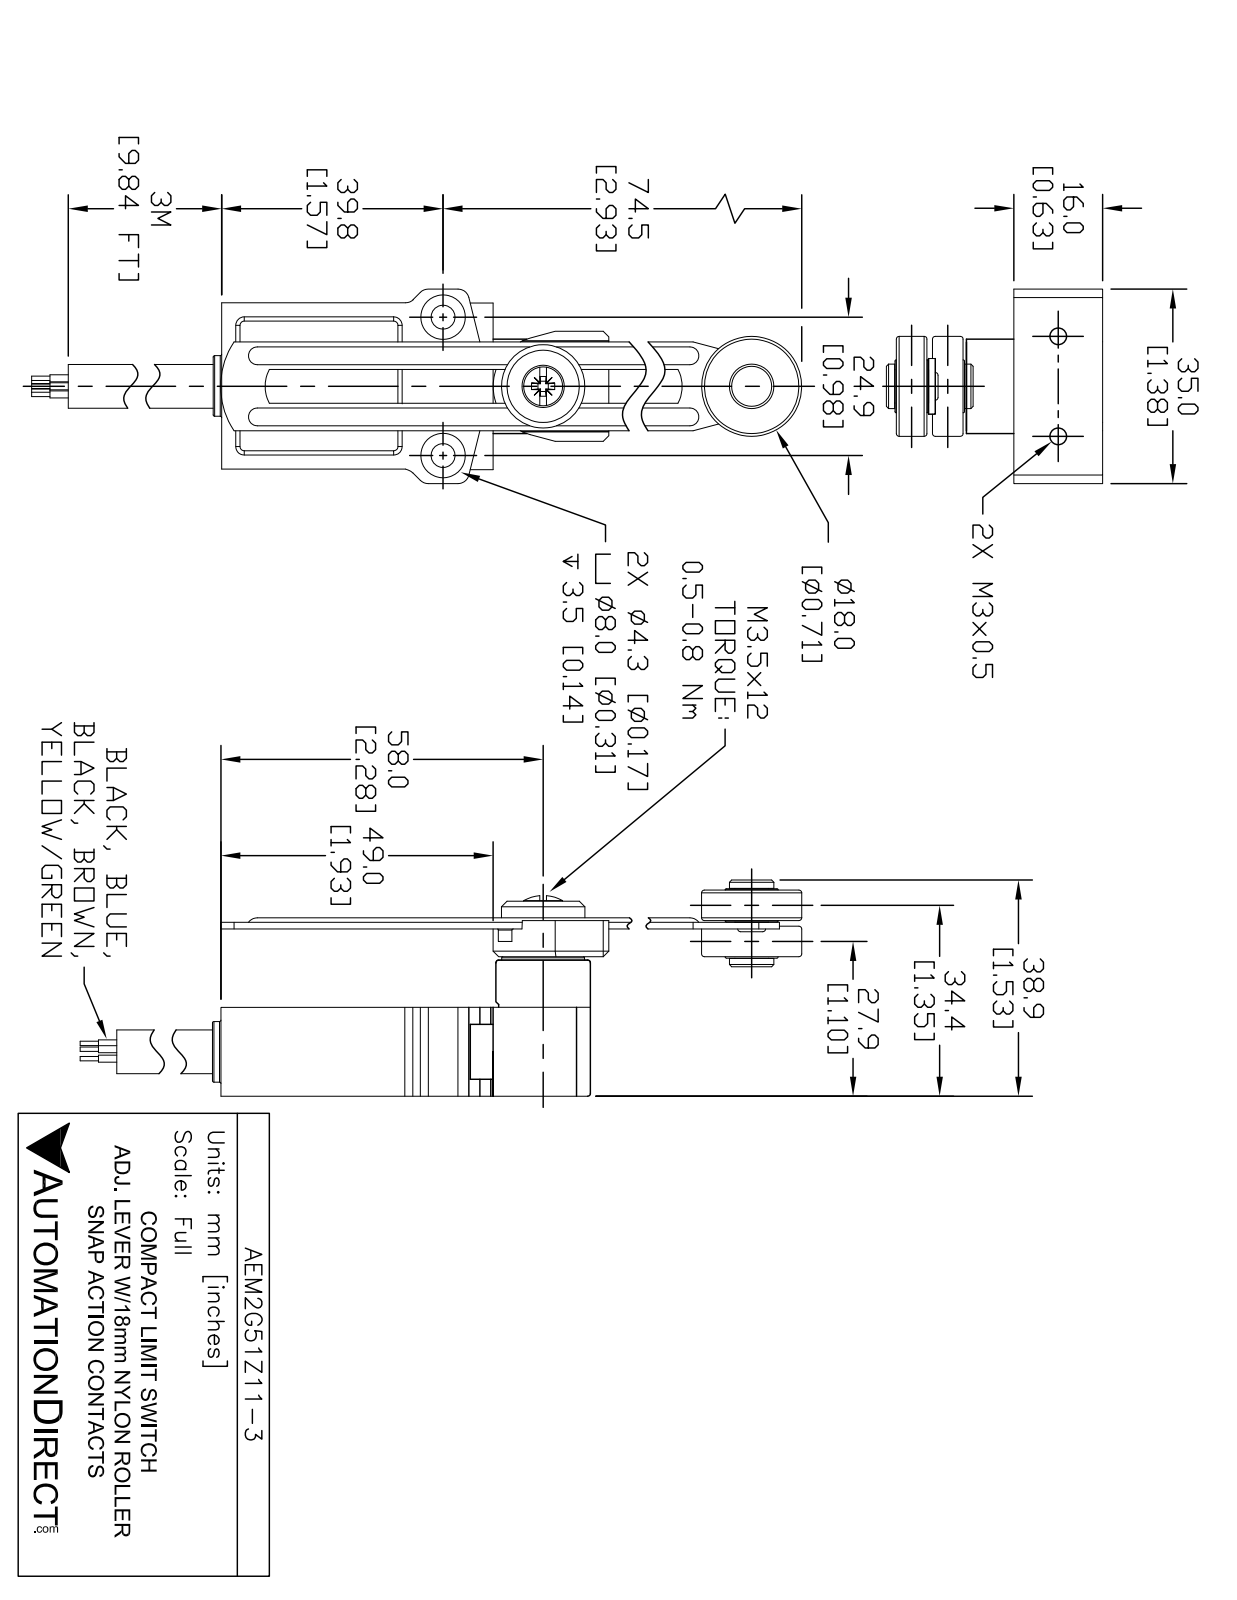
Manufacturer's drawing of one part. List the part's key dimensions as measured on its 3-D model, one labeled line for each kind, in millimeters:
Part name (STEP PRODUCT): AEM2G51Z11-3_Default
STEP written by: SolidWorks 2021 (CONFIG_CONTROL_DESIGN)
Units: millimetres
Bodies: 4 solids, 194 faces (98 planar, 75 cylindrical, 21 other)
Overall size (bounding box): 127.2 × 39.2 × 35
Volume: 33 630 mm³ · Surface area: 14 210 mm²
Round holes (diameter × count): ⌀3 ×2, ⌀4.4 ×2, ⌀8.2 ×2, ⌀5 ×1, ⌀7.6 ×1
Round bosses / shafts (diameter × count): ⌀7 ×2, ⌀18 ×1, ⌀15.8 ×1, ⌀15 ×1, ⌀9.4 ×1, ⌀7.3 ×1, ⌀6 ×1, ⌀5.4 ×1
Partial cylindrical surfaces — rounded edges, fillets, slot ends (radius × count): R2 ×8, R0.3 ×4, R1.1 ×4, R1.5 ×4, R2.1 ×4, R1.3 ×2, R6.5 ×1, R6.5 ×1
Main face-to-face distances: 16, 14.1, 30.1, 6.4, 30, 1.3, 15.3, 31.3, 9, 5.1
Hole centre spacings: 21.9, 19, 25
